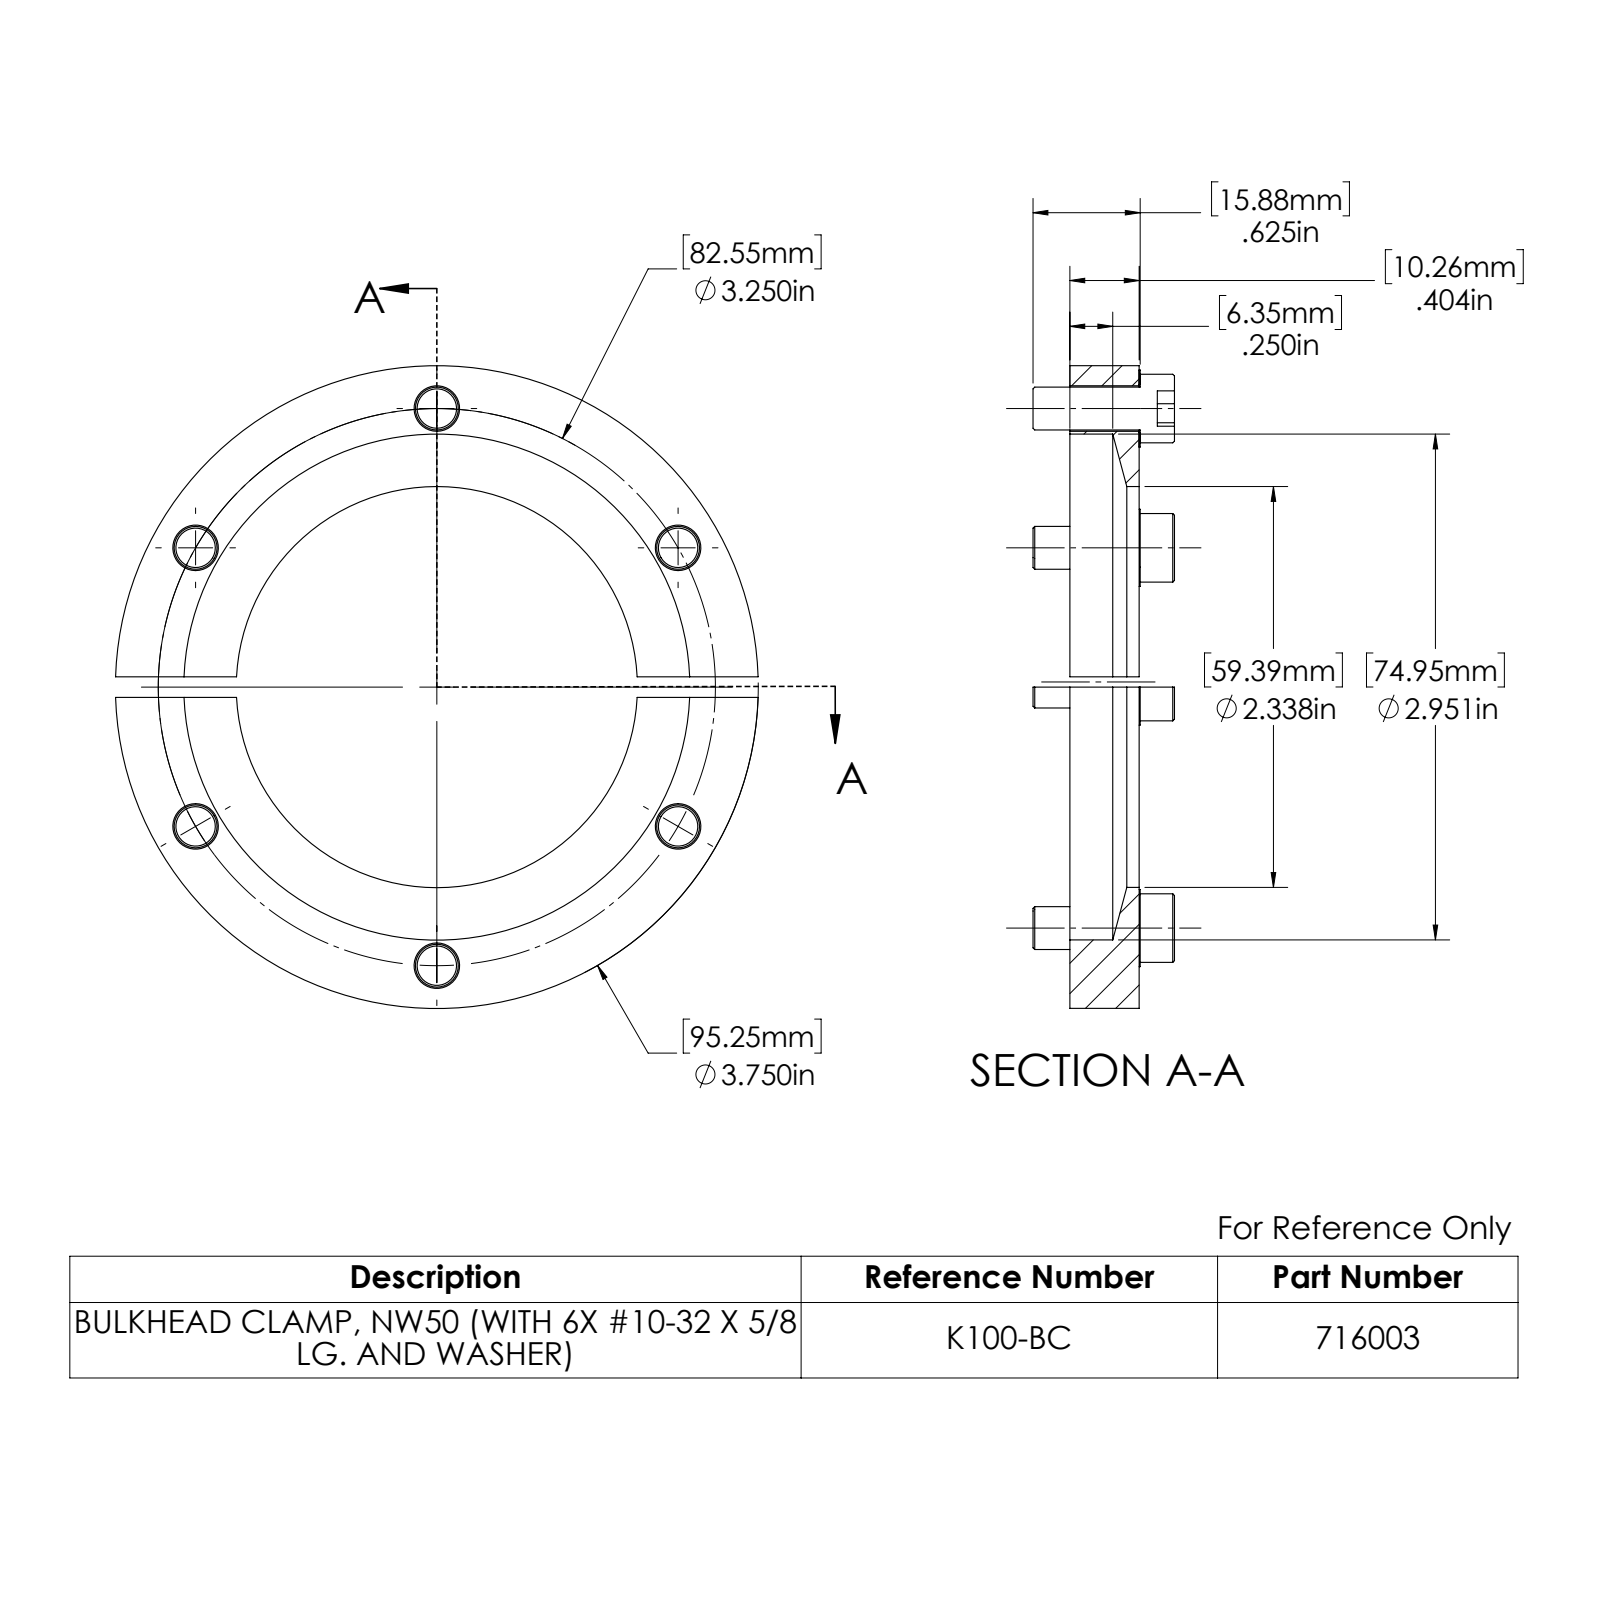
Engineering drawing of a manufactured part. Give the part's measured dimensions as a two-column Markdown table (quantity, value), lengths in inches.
| quantity | value |
| --- | --- |
| part name | 716003 |
| STEP written by | SolidWorks 2022 (AUTOMOTIVE_DESIGN) |
| units | inches |
| bodies | 8 solids, 140 faces (68 planar, 45 cylindrical, 27 other) |
| overall size | 3.75 × 3.748 × 0.954 |
| volume | 2.159 in³ |
| surface area | 29.72 in² |
| round holes (diameter × count) | 0.266 × 6, 2.34 × 1, 2.952 × 1 |
| round bosses / shafts (diameter × count) | 0.4 × 6, 0.25 × 6, 3.75 × 1 |
| main face-to-face distances | 0.404, 0.2, 0.604, 0.1, 0.12, 0.35, 0.754, 0.954, 0.854, 0.504 |
| hole center spacings | 1.625, 2.815, 1.625, 2.815, 3.25, 3.25 |
